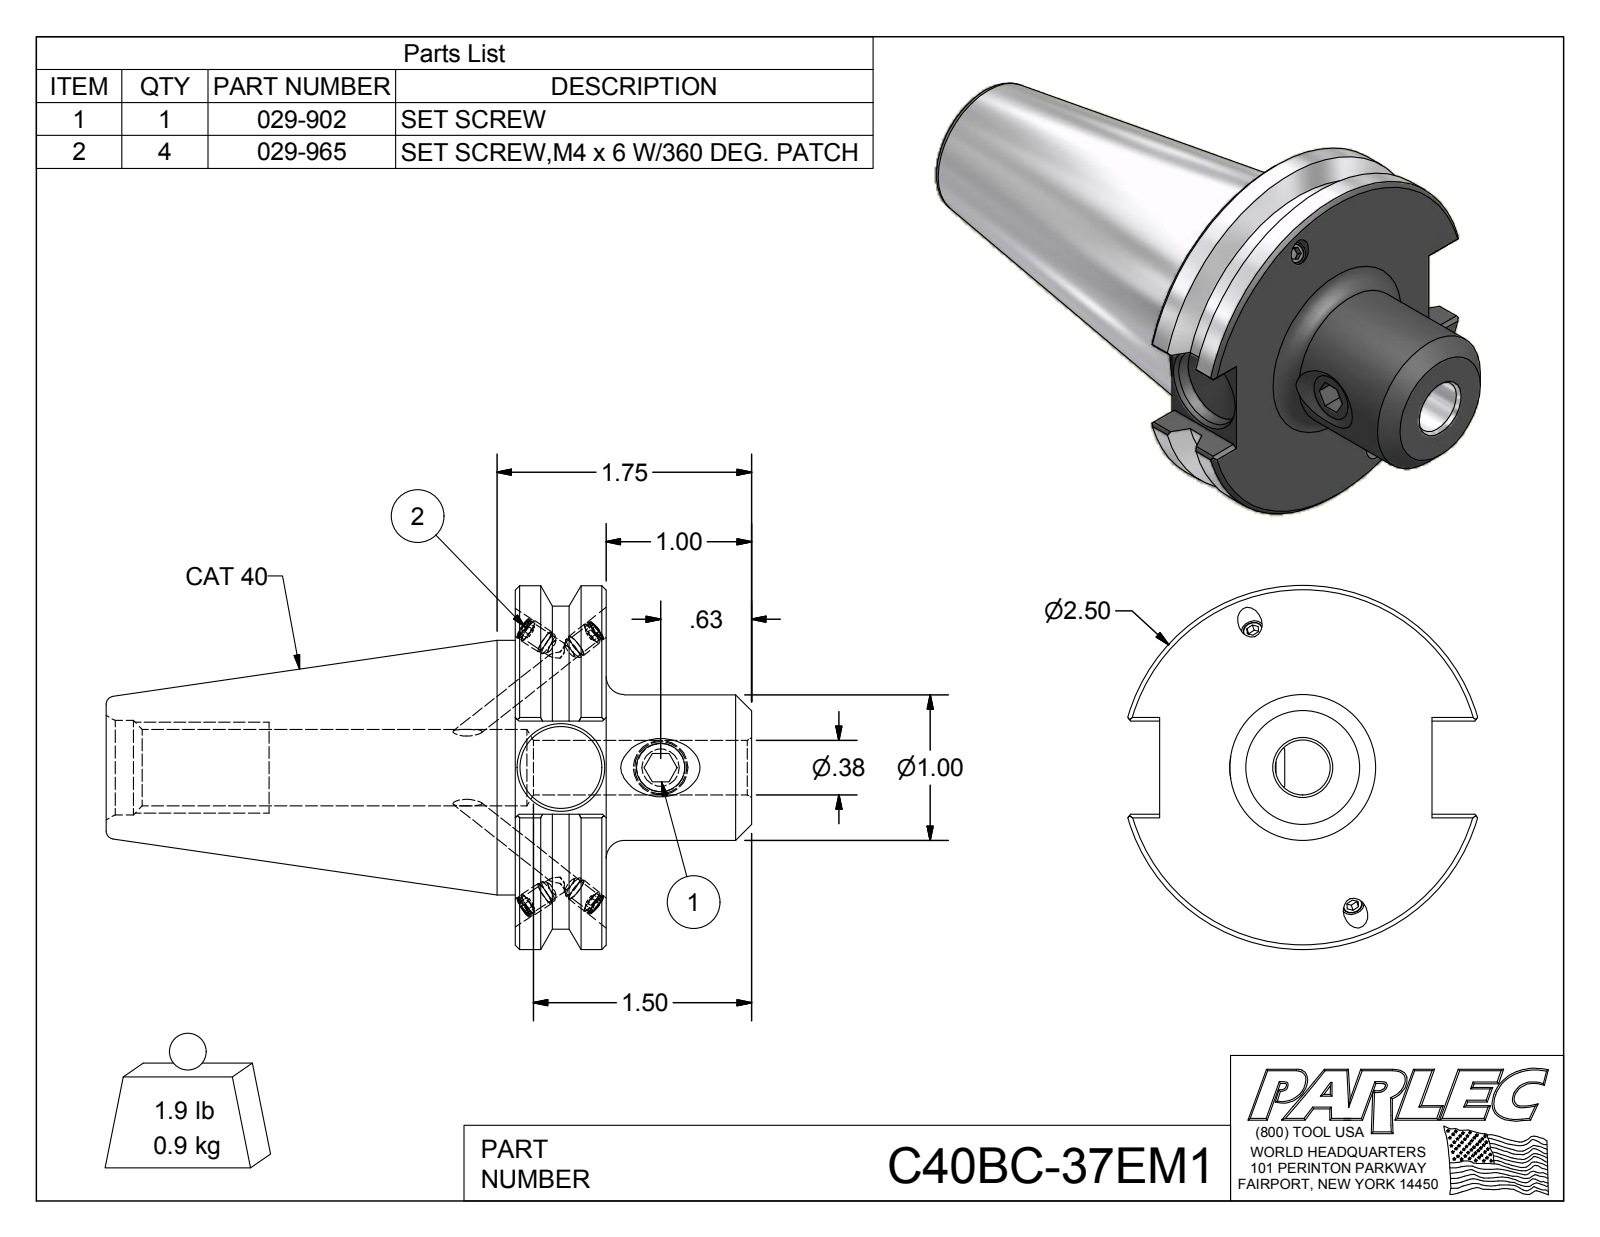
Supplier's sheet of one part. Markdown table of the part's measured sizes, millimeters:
| quantity | value |
| --- | --- |
| part name | C40BC-37EM1; C40BC-37EM1-1; 029-902; 029-965 |
| STEP written by | Autodesk Inventor 2012 (AUTOMOTIVE_DESIGN) |
| units | millimeters |
| bodies | 6 solids, 158 faces (84 planar, 35 cylindrical, 39 other) |
| overall size | 112.7 × 63.5 × 61 |
| volume | 111 700 mm³ |
| surface area | 24 430 mm² |
| round holes (diameter × count) | 3.3 × 4, 4.1 × 4, 8 × 1, 8.4 × 1, 9.5 × 1, 10.1 × 1, 13.4 × 1, 16.5 × 1 |
| round bosses / shafts (diameter × count) | 4.2 × 4, 4 × 4, 63.5 × 1, 56.4 × 1, 43.9 × 1, 25.4 × 1, 9.5 × 1 |
| main face-to-face distances | 15.9, 41.3, 25.4, 16.3, 47.2, 6, 71.5, 87.3, 112.7, 81.3 |
| hole center spacings | 17.4 |
